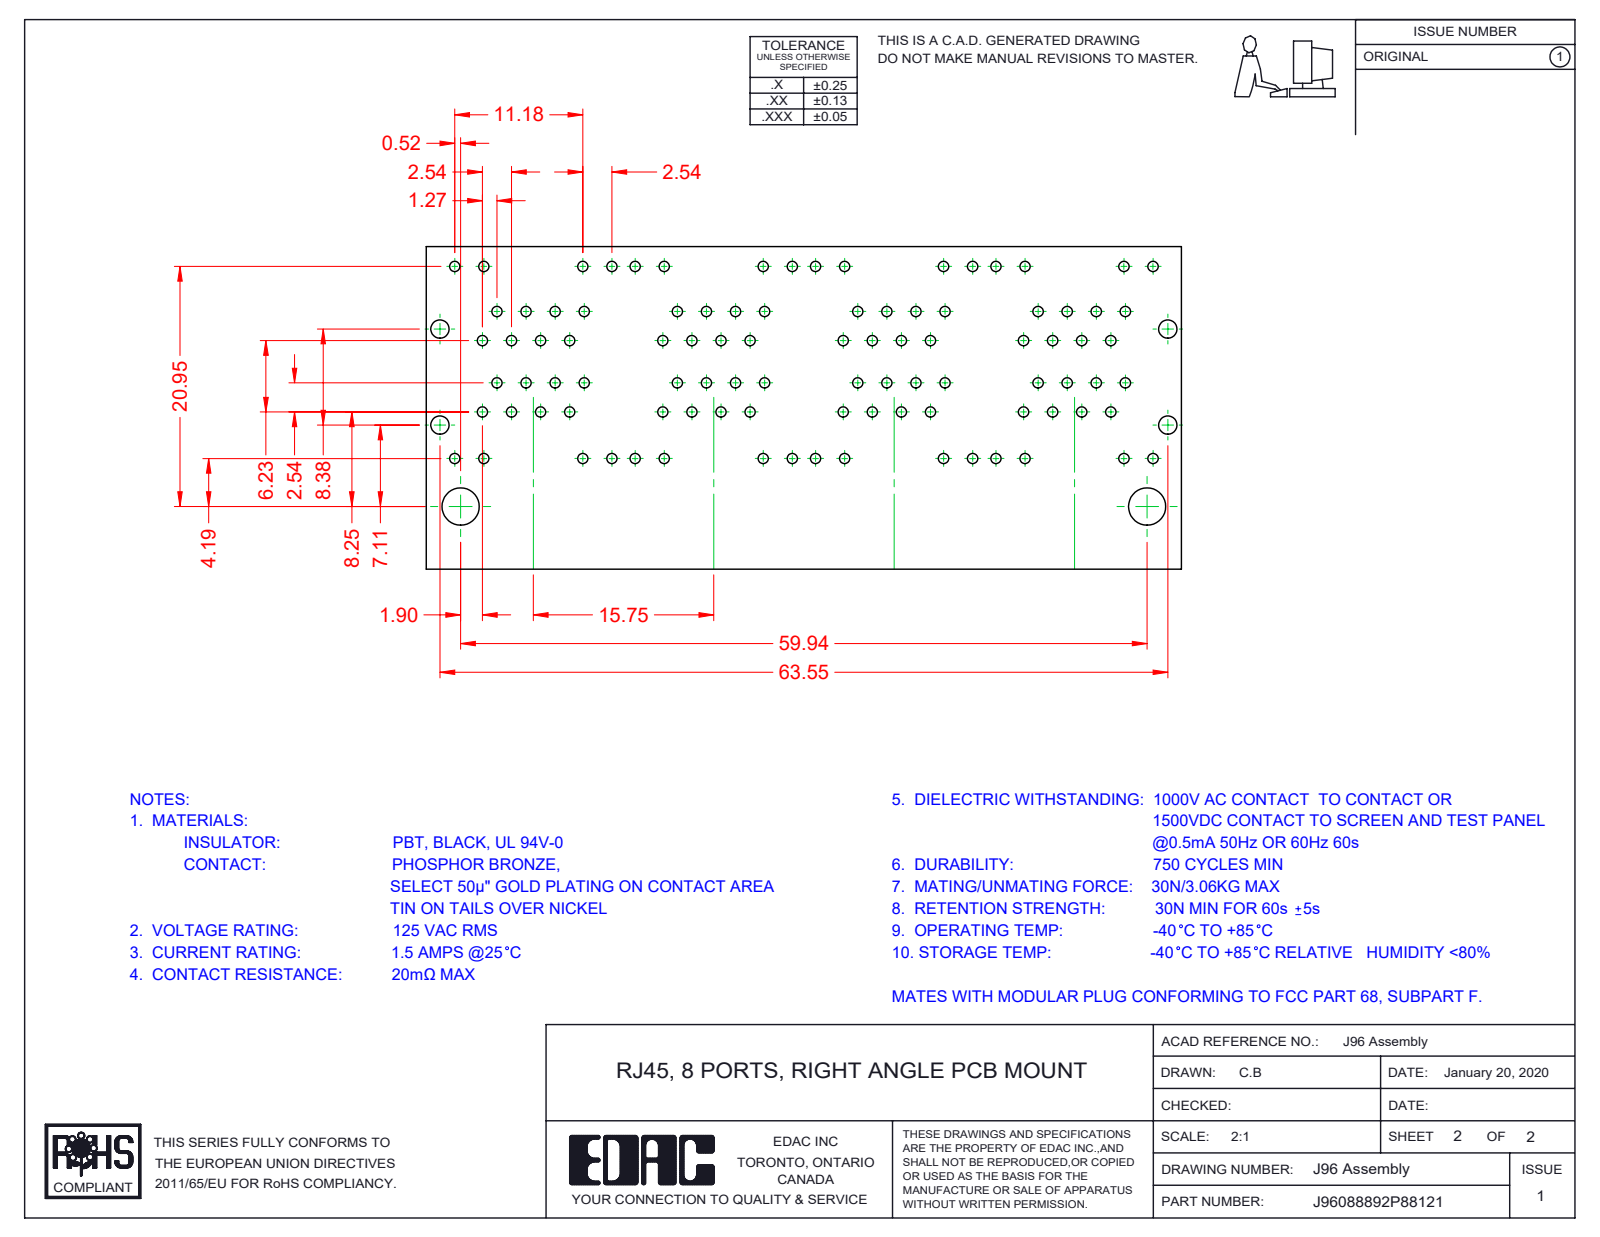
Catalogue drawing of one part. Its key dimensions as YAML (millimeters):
part_name: "96 Shield_8 Ports LED - No EMI; 96 Contact Lock Lower; 96 LED RH Upper_8-Red-Yellow; J96088892P88121 (+8 more)"
step_written_by: "SolidWorks 2016 (CONFIG_CONTROL_DESIGN)"
units: millimeters
bodies: {solids: 96, faces: 7674, planar: 6069, cylindrical: 1339, other: 266}
overall_size: [64.05, 29.58, 28.68]
volume: 24160
surface_area: 63658
round_holes:
  - {diameter: 1.7, count: 3}
round_bosses_or_shafts:
  - {diameter: 1.68, count: 3}
partial_cylinders:
  - {radius: 0.25, count: 124}
  - {radius: 0.35, count: 73}
  - {radius: 1, count: 72}
  - {radius: 0.5, count: 49}
  - {radius: 0.91, count: 32}
  - {radius: 0.2, count: 21}
  - {radius: 0.7, count: 11}
  - {radius: 0.22, count: 8}
face_to_face_distances: [15.75, 0.35, 9.95, 1.17, 1.6, 0.54, 9.98, 10.18, 12.67, 3.37]
hole_center_spacings: [15.75, 31.5]
